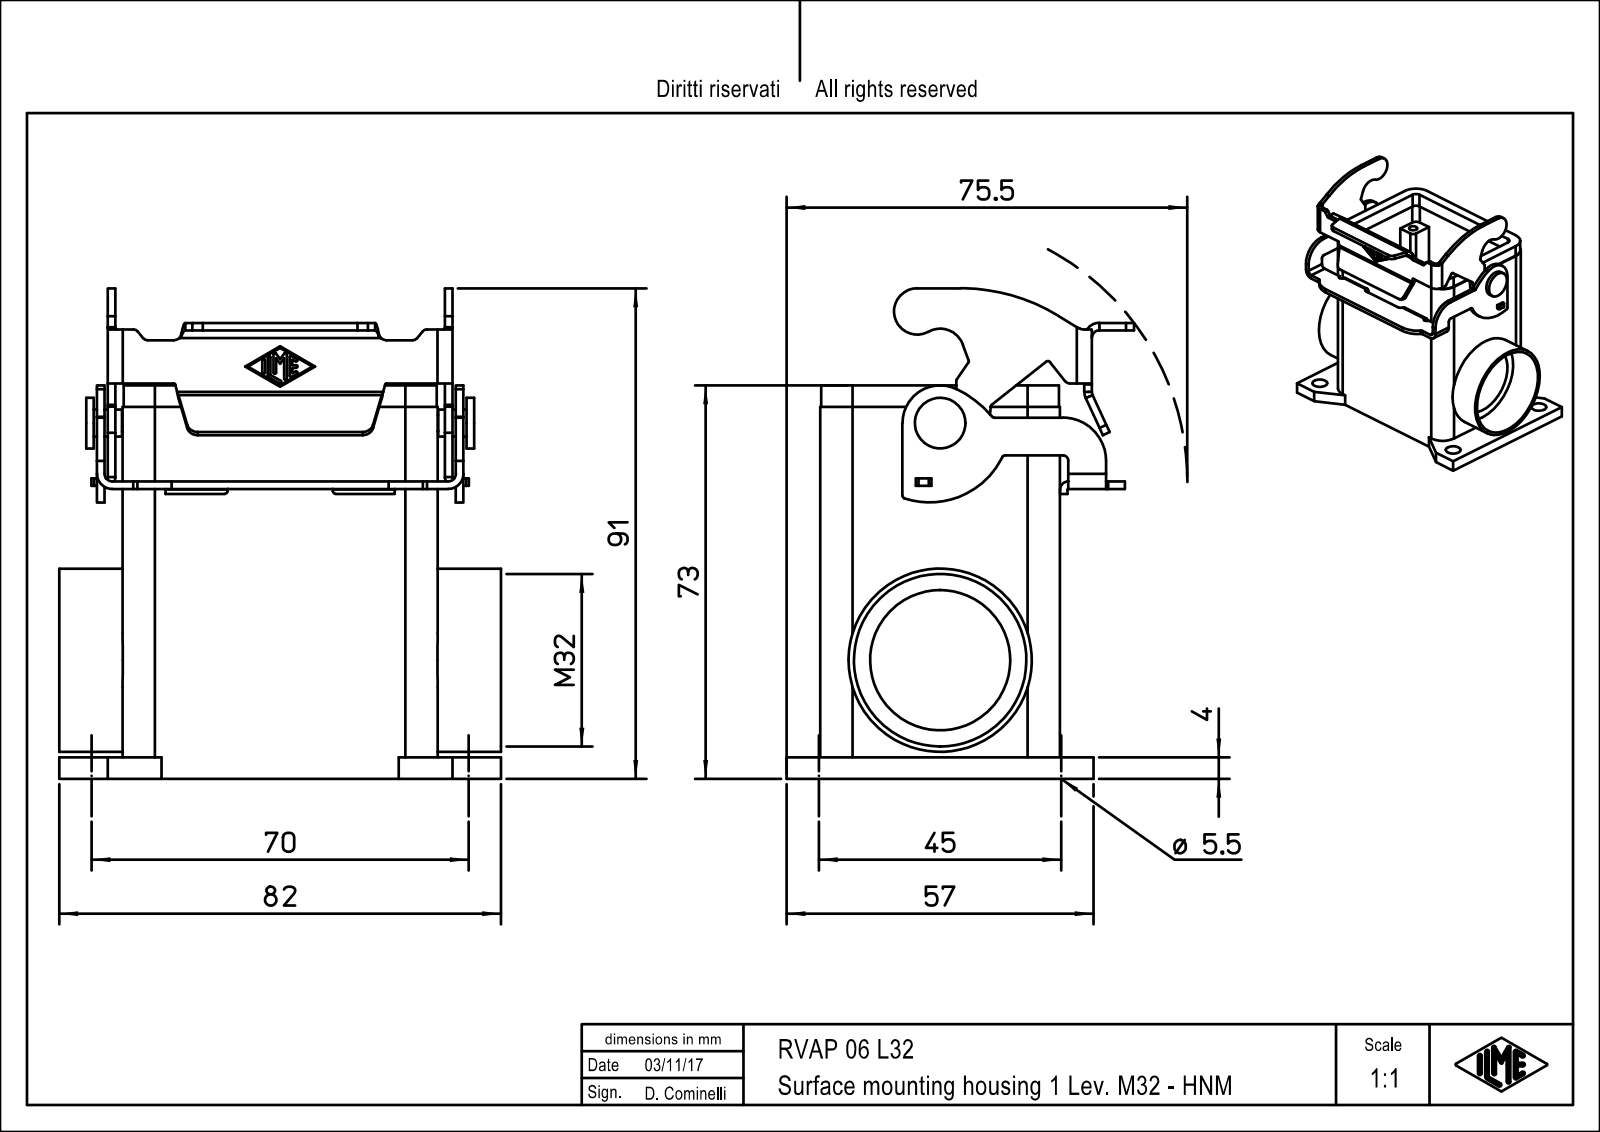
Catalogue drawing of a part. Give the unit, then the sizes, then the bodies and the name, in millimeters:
Units: millimetres
Overall size (bounding box): 91 × 82 × 64.48
Round holes (diameter × count): ⌀2.46 ×4, ⌀3 ×4, ⌀5.5 ×4, ⌀26 ×1, ⌀32 ×1
Round bosses / shafts (diameter × count): ⌀34 ×1, ⌀9.4 ×1, ⌀5 ×1, ⌀3 ×1
Partial cylindrical surfaces — rounded edges, fillets, slot ends (radius × count): R0.25 ×16, R0.5 ×12, R1 ×12, R1.5 ×11, R2 ×8, R1.4 ×6, R2.8 ×6, R1.8 ×4
Main face-to-face distances: 4, 40.5, 44.5, 1.4, 36.5, 6.75, 10.75, 47.75, 2, 64.6
Hole centre spacings: 15.81, 38.28, 57.71, 67.42, 27, 44, 45, 51.62
Volume: 85 514 mm³ · Surface area: 49 161 mm²
Bodies: 1 solid, 383 faces (201 planar, 170 cylindrical, 12 other)
Part name (STEP PRODUCT): RVAP_06_L32
STEP written by: PTC Creo Elements/Direct Modeling 19.0E 27-Jun-2016 (C) Parametric Technology GmbH (AUTOMOTIVE_DESIGN)
